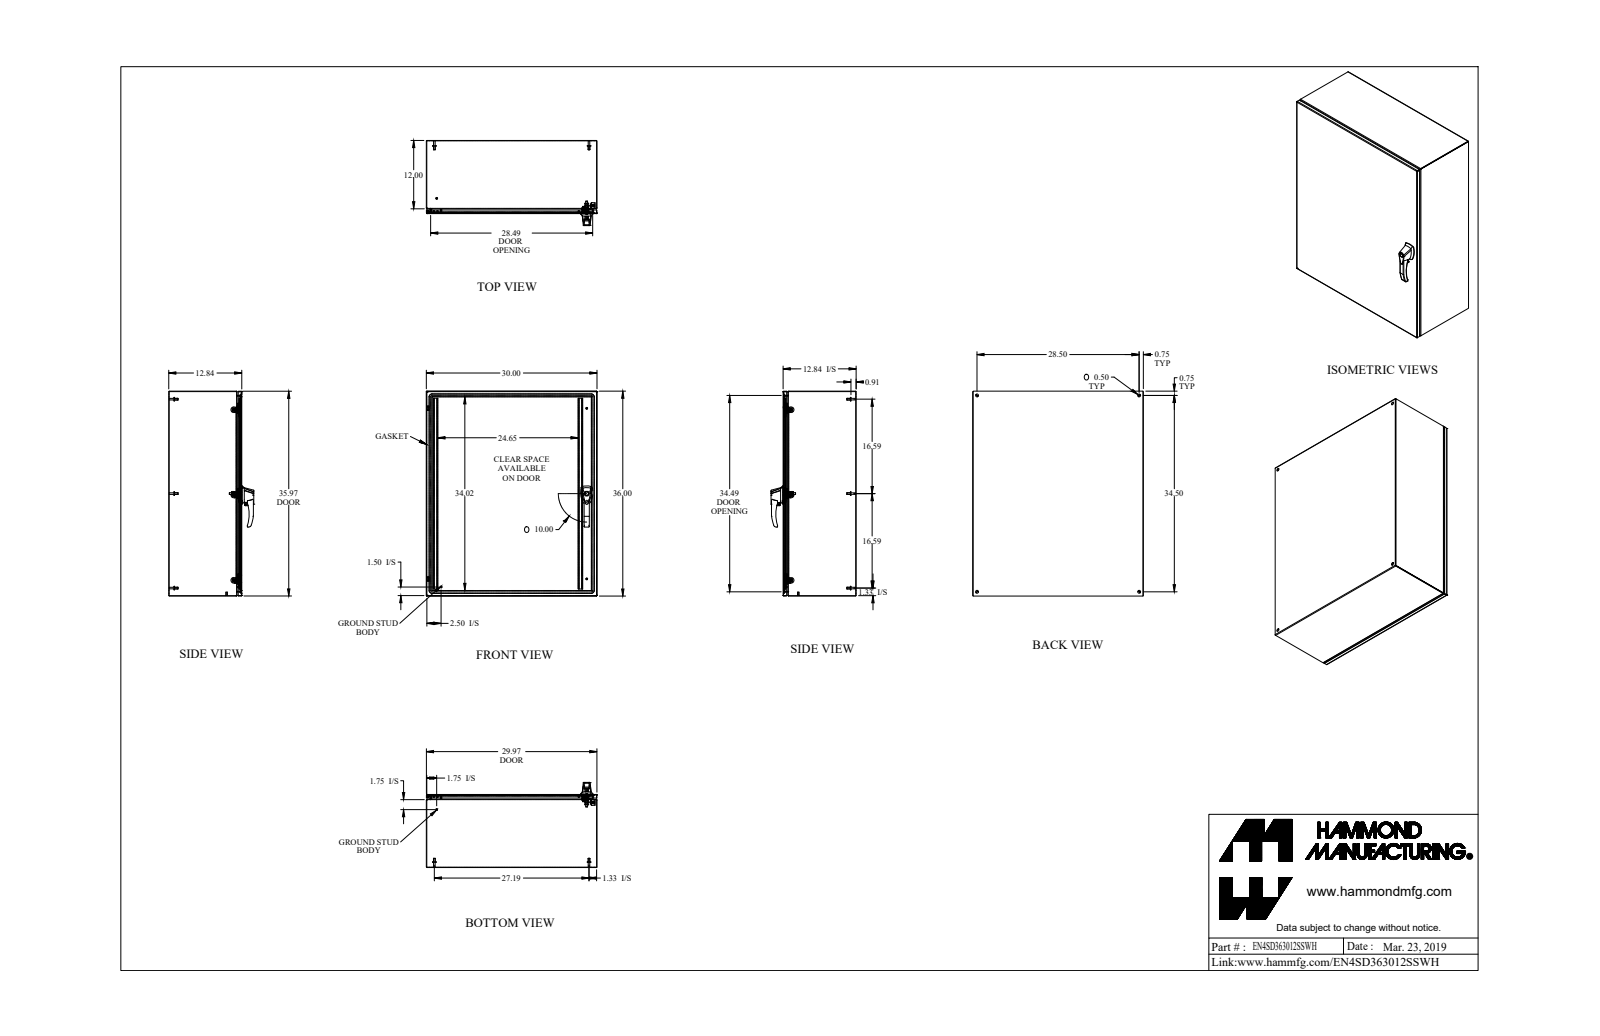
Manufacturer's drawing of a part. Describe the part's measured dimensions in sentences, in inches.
The part is named "EN4SD363012SSWH". Its 3-D file was written by "SolidWorks 2019 (AUTOMOTIVE_DESIGN)". It is 56 solids with 1391 faces: 602 planar, 537 cylindrical and 252 other. Overall it measures 36 by 30 by 14.958 inches. Its volume is 320.7 cubic inches and its surface area 8 680 square inches. Round holes: 6 of diameter 0.176, 4 of diameter 0.5, 3 of diameter 0.25, 3 of diameter 0.265, 3 of diameter 0.313, 3 of diameter 0.413, 2 of diameter 0.196, 2 of diameter 0.256, 2 of diameter 0.394, 1 of diameter 0.172, 1 of diameter 0.233, 1 of diameter 0.24. Round bosses or shafts: 8 of diameter 0.313, 7 of diameter 0.25, 6 of diameter 0.375, 6 of diameter 0.275, 6 of diameter 0.156, 4 of diameter 0.625, 3 of diameter 1, 3 of diameter 0.51. Partial cylindrical surfaces (rounded edges, fillets, slot ends): 18 of radius 0.036, 18 of radius 0.108, 13 of radius 0.25, 12 of radius 0.01, 12 of radius 0.048, 9 of radius 0.125, 7 of radius 0.06, 6 of radius 0.006. The main face-to-face distances are 0.072, 12.771, 12.699, 12.843, 29.928, 35.928, 29.856, 30, 35.856, 36. The hole center spacings are 0.786, 14.984, 14.985, 15, 27.532, 28.5, 29.969, 34.5.
